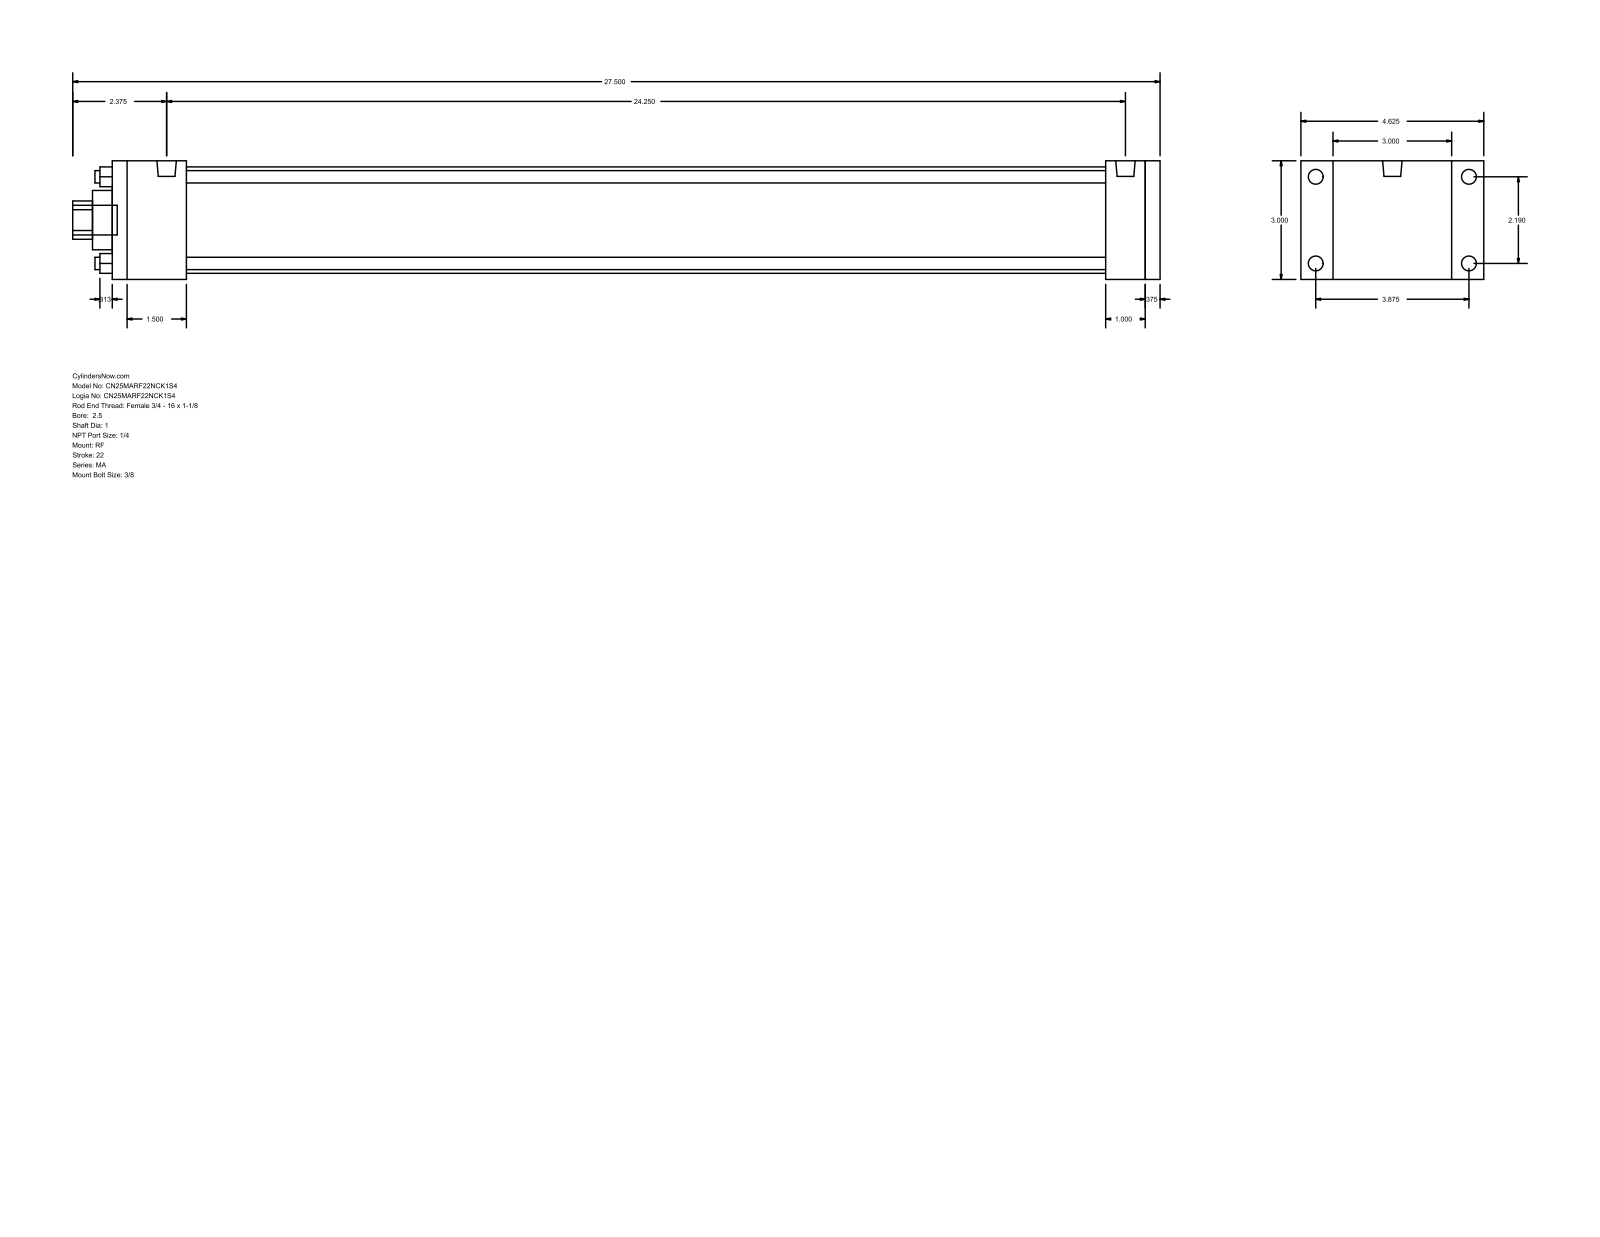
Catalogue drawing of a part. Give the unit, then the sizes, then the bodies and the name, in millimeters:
Units: millimetres
Overall size (bounding box): 698.5 × 117.47 × 76.2
Round holes (diameter × count): ⌀7.94 ×4, ⌀25.4 ×1, ⌀38.1 ×1, ⌀68.33 ×1
Round bosses / shafts (diameter × count): ⌀9.53 ×4, ⌀7.94 ×4, ⌀12.49 ×2, ⌀19.05 ×1
Partial cylindrical surfaces — rounded edges, fillets, slot ends (radius × count): R12.29 ×1
Main face-to-face distances: 76.2, 673.1, 663.58, 9.52, 25.4, 47.63, 638.18, 590.55, 615.95, 625.47
Hole centre spacings: 39.33, 55.62, 78.66
Bodies: 0 solids, 92 faces (64 planar, 28 cylindrical, 0 other)
Part name (STEP PRODUCT): MA_RF__0250_1
STEP written by: GSSL Pune (CONFIG_CONTROL_DESIGN)
